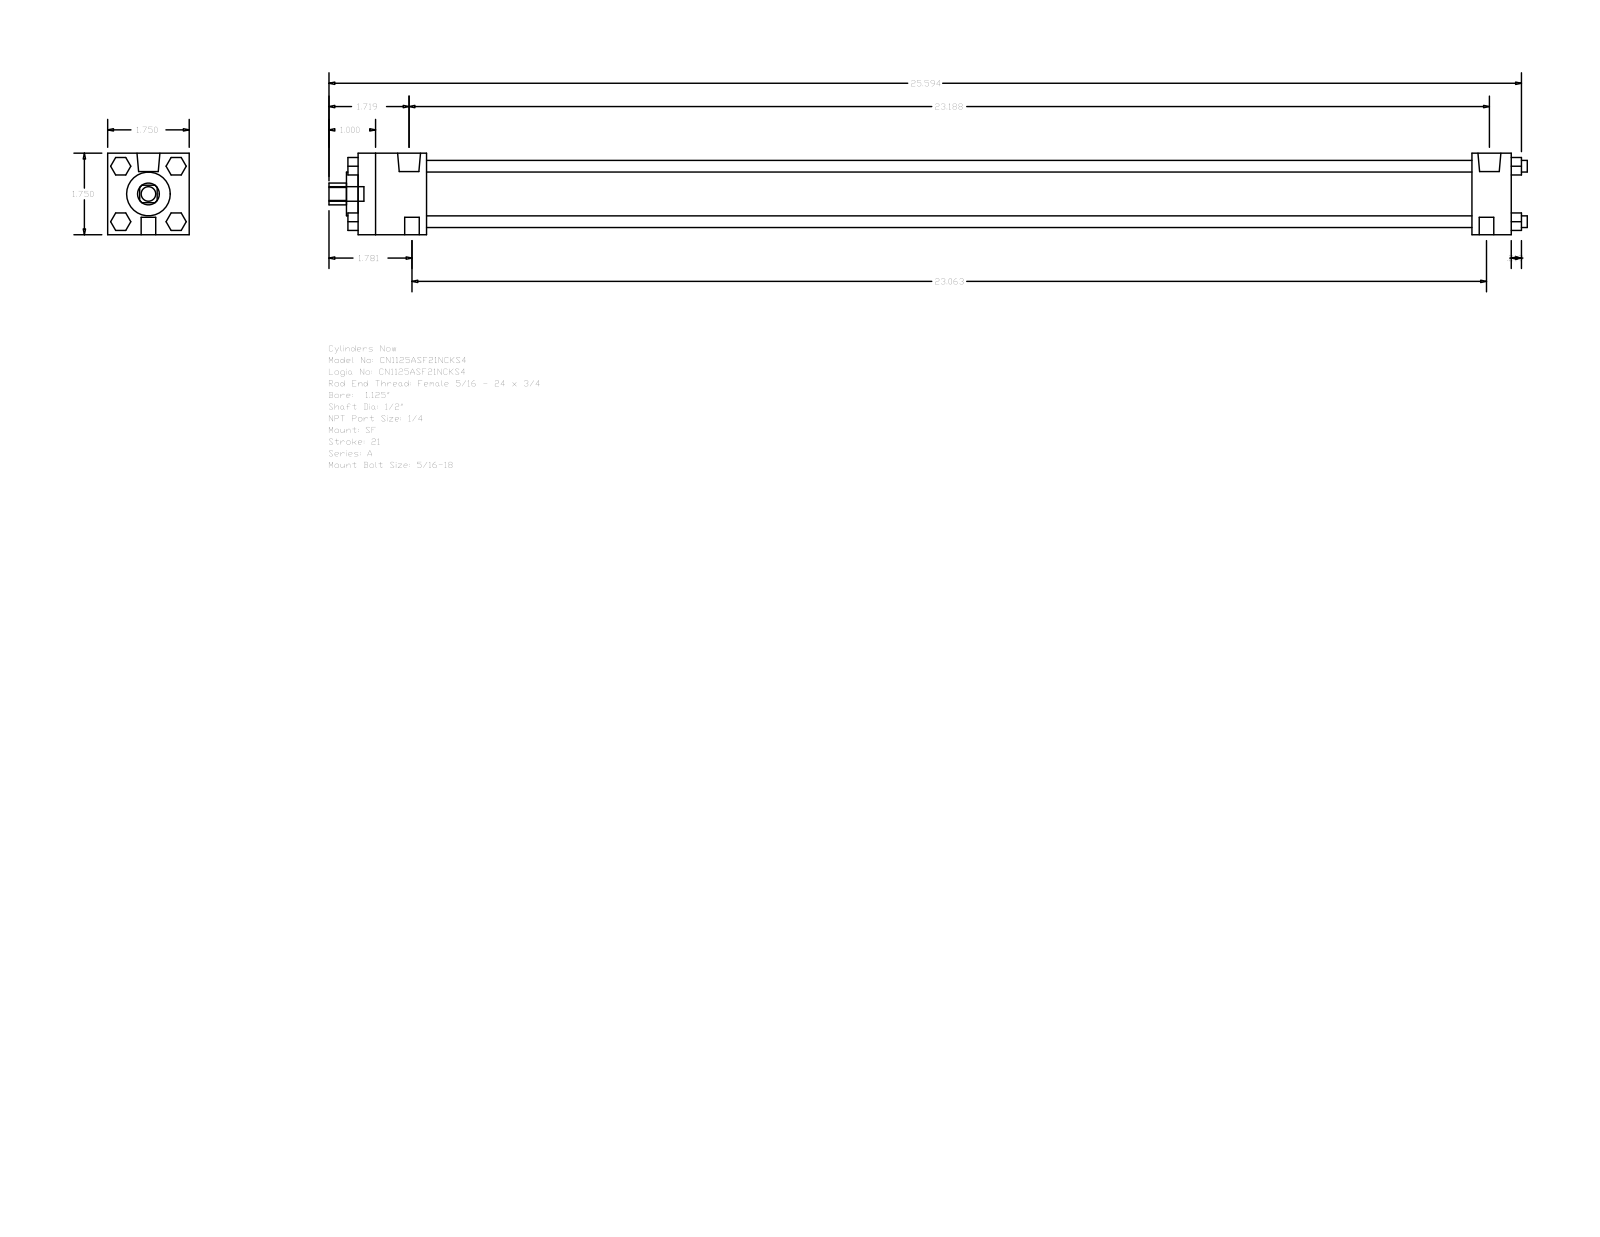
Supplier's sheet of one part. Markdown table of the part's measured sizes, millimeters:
| quantity | value |
| --- | --- |
| part name | A_SF__0112_0.5 |
| STEP written by | GSSL Pune (CONFIG_CONTROL_DESIGN) |
| units | millimeters |
| bodies | 0 solids, 120 faces (92 planar, 28 cylindrical, 0 other) |
| overall size | 653.26 × 44.45 × 44.45 |
| round holes (diameter × count) | 12.7 × 1, 23.81 × 1, 31.88 × 1 |
| round bosses / shafts (diameter × count) | 6.35 × 4, 7.94 × 3, 12.49 × 2, 5.56 × 2 |
| partial cylindrical surfaces (radius × count) | 5.94 × 1 |
| main face-to-face distances | 44.46, 628.64, 607.21, 21.43, 37.3, 569.91, 591.34, 9.53, 5.59, 9.52 |
